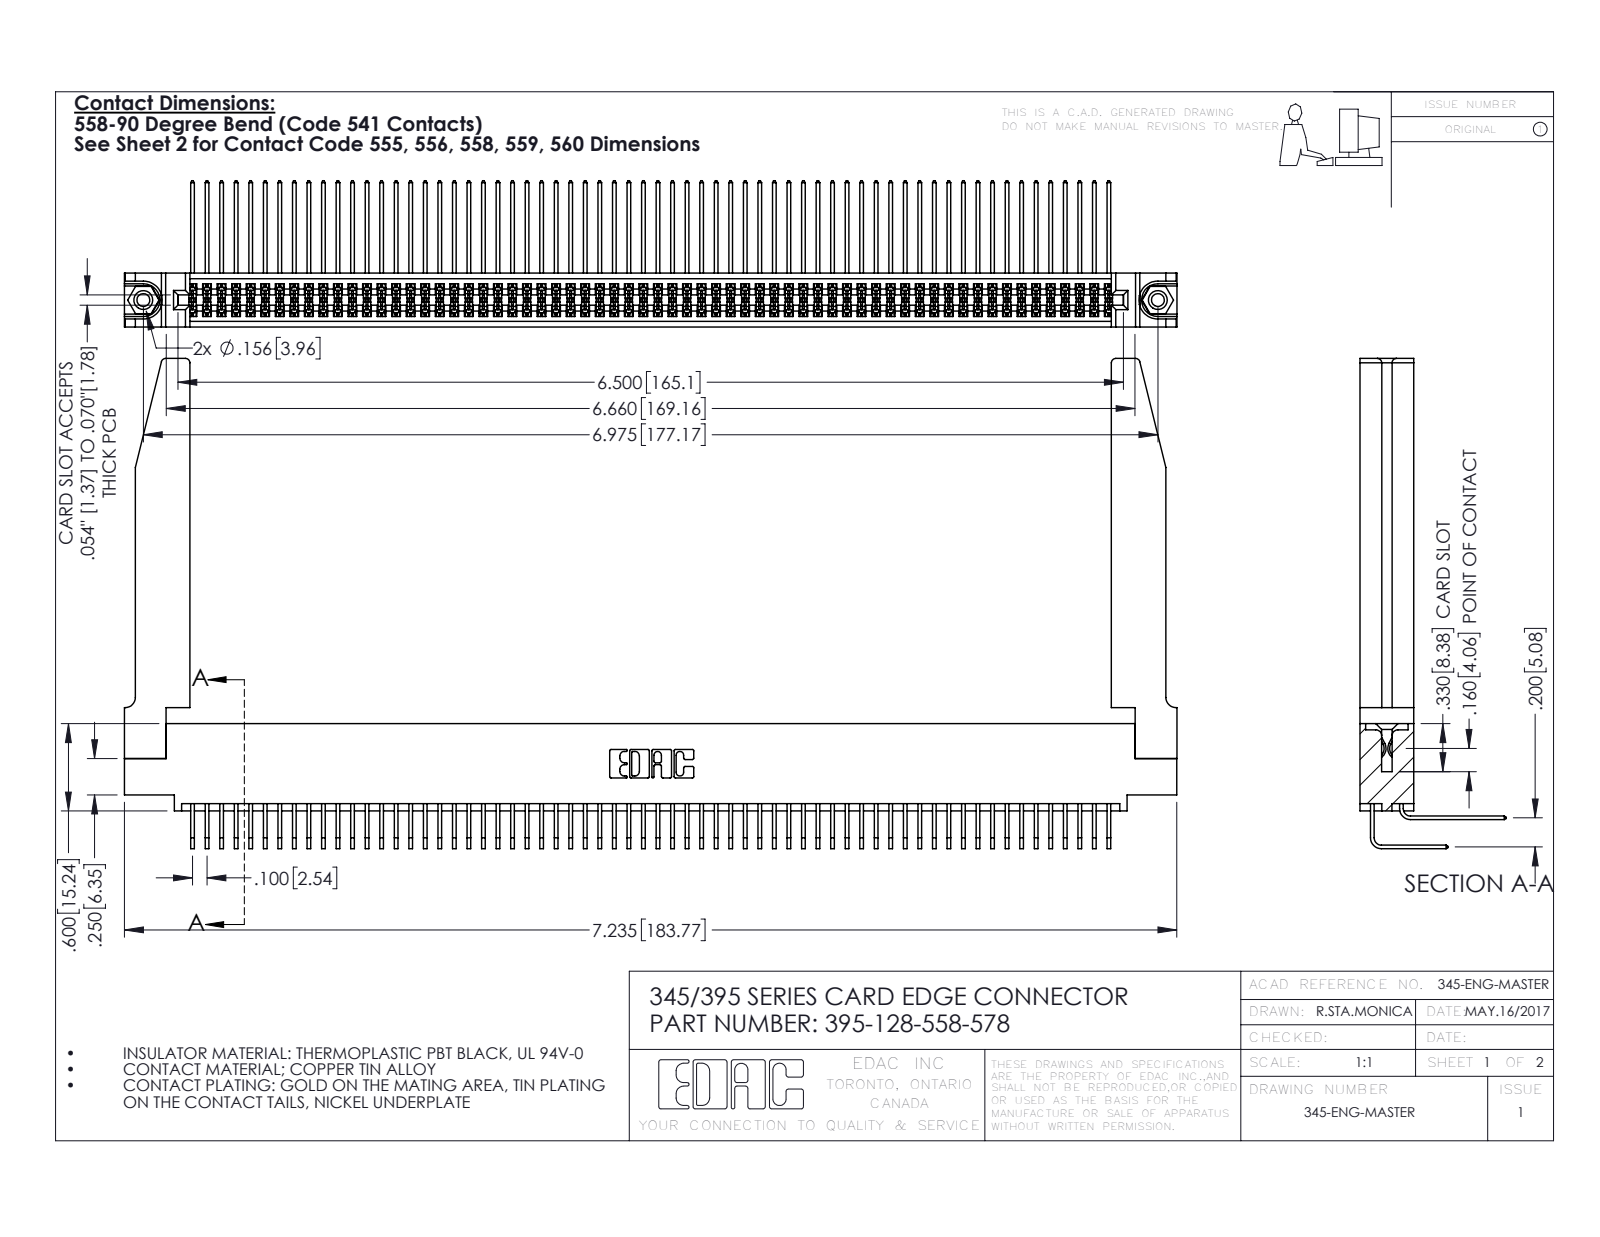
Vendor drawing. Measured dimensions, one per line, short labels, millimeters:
name: 345-220-078_345-220-078; 345 Part_0.110 Offset - 0.156 Dia-TH; 345-292-001_558 Tail - 2; 345-292-001_558 559 Tail - 1 (+2 more)
written by: SolidWorks 2016 (CONFIG_CONTROL_DESIGN)
unit: mm
bodies: 133 solids, 7020 faces (4706 planar, 2262 cylindrical, 52 other)
size: 183.8 × 85.6 × 25.5
volume: 26 500 mm³; area: 38 500 mm²
holes: 2× ⌀2.3, 2× ⌀3.2, 2× ⌀4, 1× ⌀1.6
bosses: 2× ⌀3.9
rounds: 193× R0.2, 22× R0.3, 8× R0.8, 6× R0.2, 6× R0.8, 3× R0.7, 2× R0.4, 2× R0.5
face distances: 1.8, 7.6, 9.4, 5.1, 2.5, 6.9, 0.6, 5.7, 0.6, 4.4
hole spacings: 6.9, 171.2, 177.2
